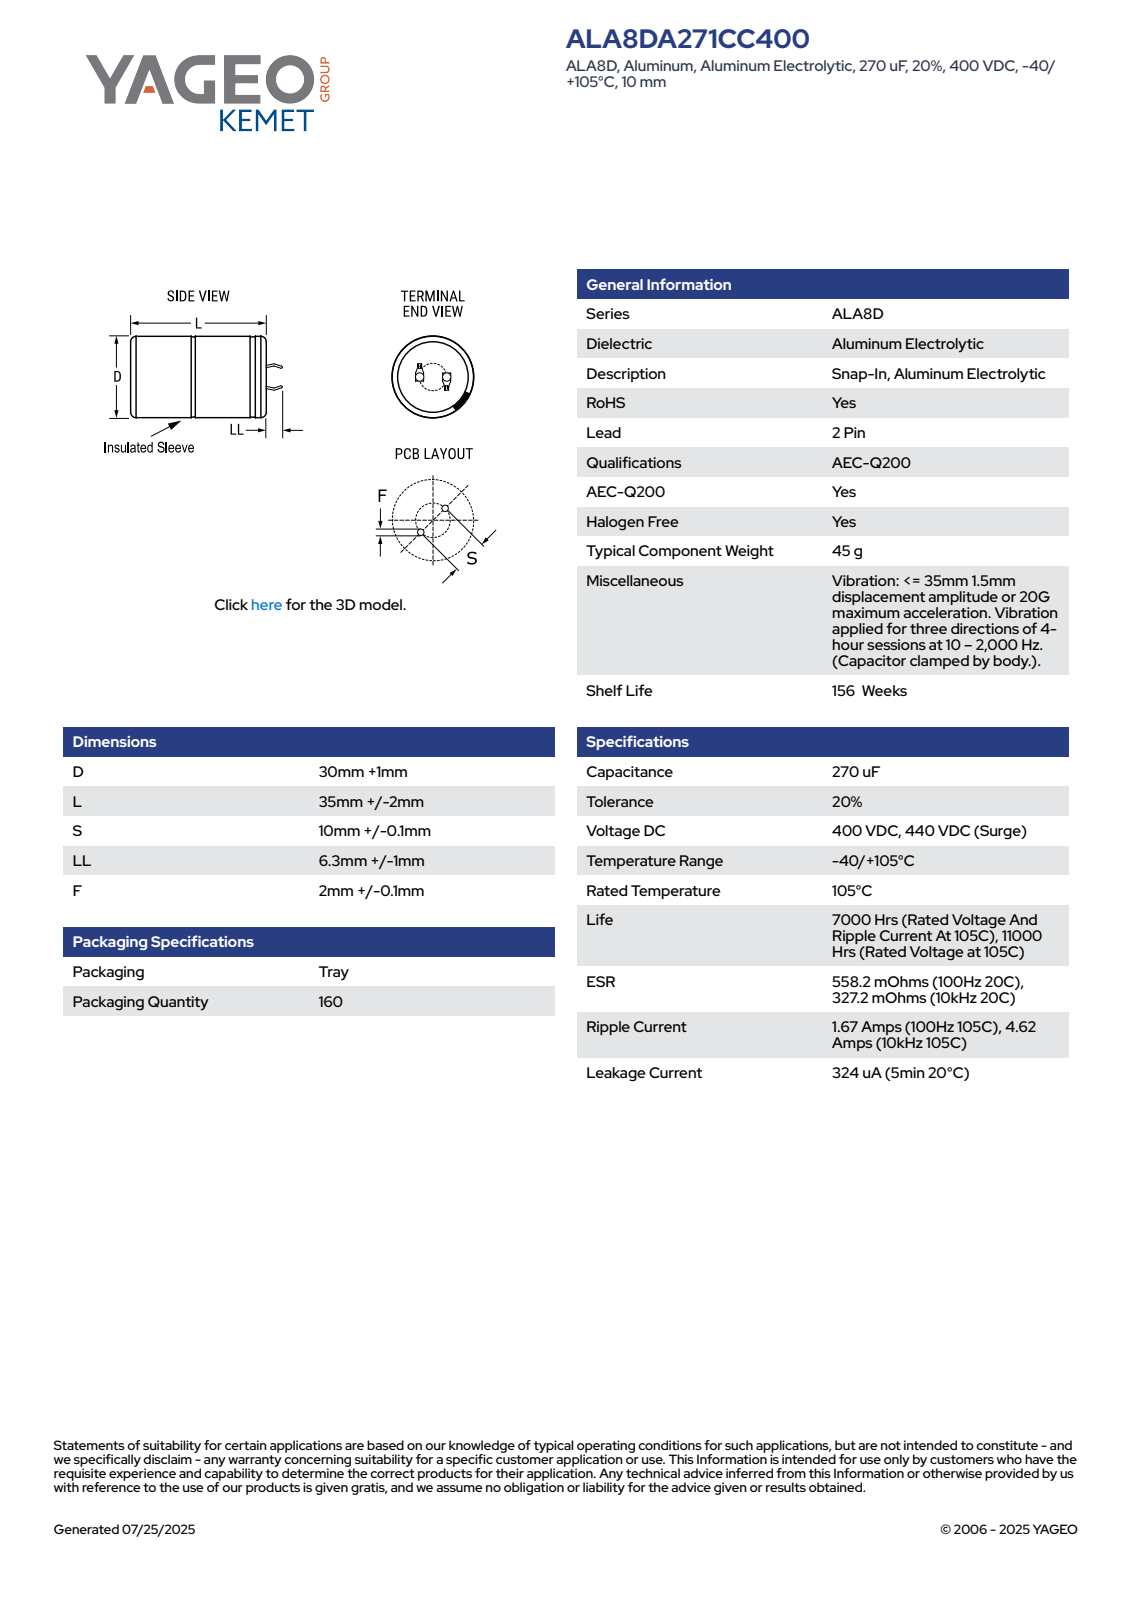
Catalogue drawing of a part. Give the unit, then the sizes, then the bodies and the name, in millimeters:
Units: millimetres
Overall size (bounding box): 44.29 × 31 × 31
Round holes (diameter × count): ⌀27.43 ×1
Round bosses / shafts (diameter × count): ⌀31 ×1
Partial cylindrical surfaces — rounded edges, fillets, slot ends (radius × count): R15.49 ×1
Main face-to-face distances: 36.99, 0.6, 37.49, 0.5, 7.08, 7.64, 1.35, 0.75, 7.68, 6.48
Volume: 27 555 mm³ · Surface area: 5 175 mm²
Bodies: 1 solid, 106 faces (52 planar, 11 cylindrical, 43 other)
Part name (STEP PRODUCT): CARS_K2PAV_30X35_D31L37S10LL7.3F2.1
STEP written by: SolidWorks 2021 (AUTOMOTIVE_DESIGN)
